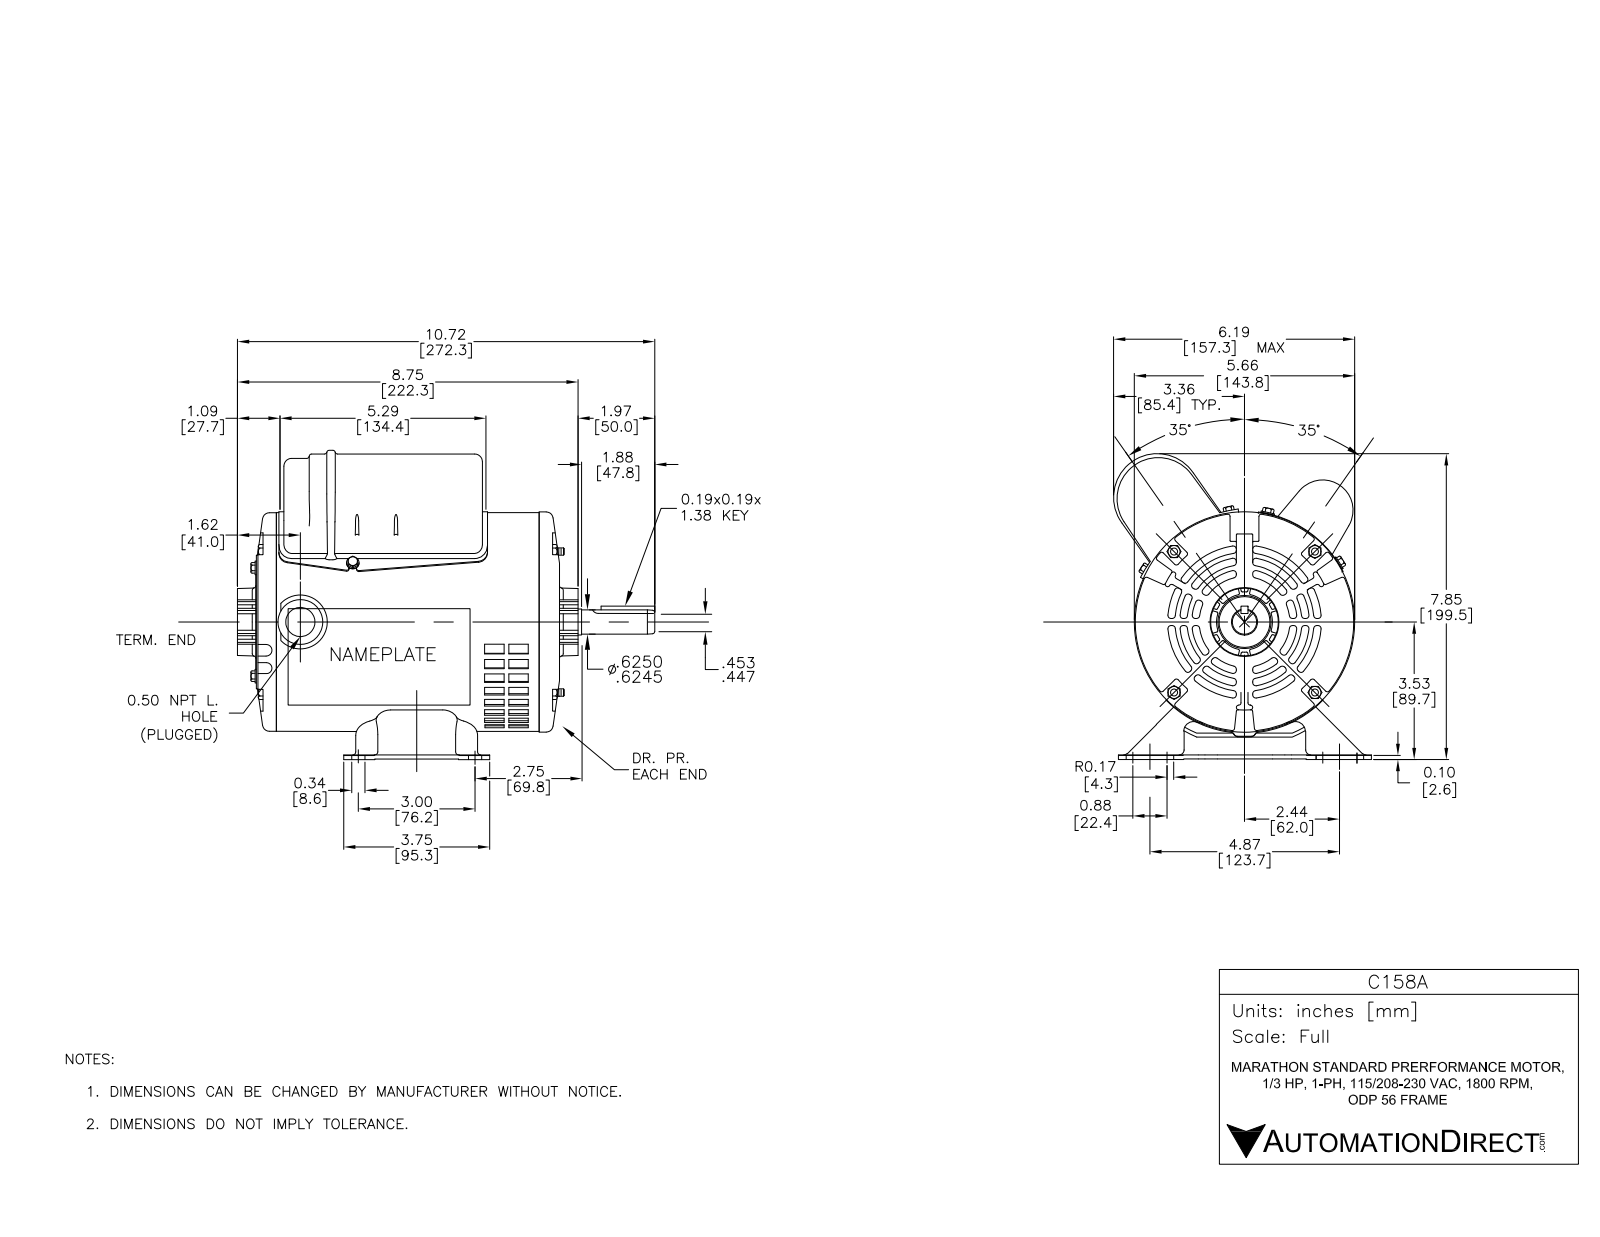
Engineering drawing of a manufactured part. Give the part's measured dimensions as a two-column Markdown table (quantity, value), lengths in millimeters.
| quantity | value |
| --- | --- |
| part name | C158A SS404114-700_RevA |
| STEP written by | SolidWorks 2017 (AUTOMOTIVE_DESIGN) |
| units | millimeters |
| bodies | 29 solids, 4278 faces (1485 planar, 836 cylindrical, 1957 other) |
| overall size | 278.6 × 192.4 × 165.1 |
| volume | 488 000 mm³ |
| surface area | 459 900 mm² |
| round holes (diameter × count) | 3.9 × 11, 6.4 × 5, 4.9 × 4, 5.6 × 4, 5.5 × 2, 7.1 × 2, 11.6 × 1, 12.8 × 1, 16.3 × 1, 17 × 1, 17.4 × 1, 18.5 × 1 |
| round bosses / shafts (diameter × count) | 4.2 × 6, 10.1 × 4, 8.8 × 4, 4.8 × 4, 4.2 × 4, 8.5 × 2, 142.7 × 1, 142.6 × 1 |
| partial cylindrical surfaces (radius × count) | 1.5 × 52, 0.8 × 35, 0.4 × 32, 0.5 × 27, 6.4 × 25, 1.3 × 20, 4.3 × 18, 2.3 × 16 |
| main face-to-face distances | 0.7, 2.6, 194.6, 129.9, 191.3, 13.5, 0.4, 2.3, 195.6, 1 |
| hole center spacings | 65.1, 92, 30.2, 61, 65.5, 107.8, 122.4, 130.1 |
